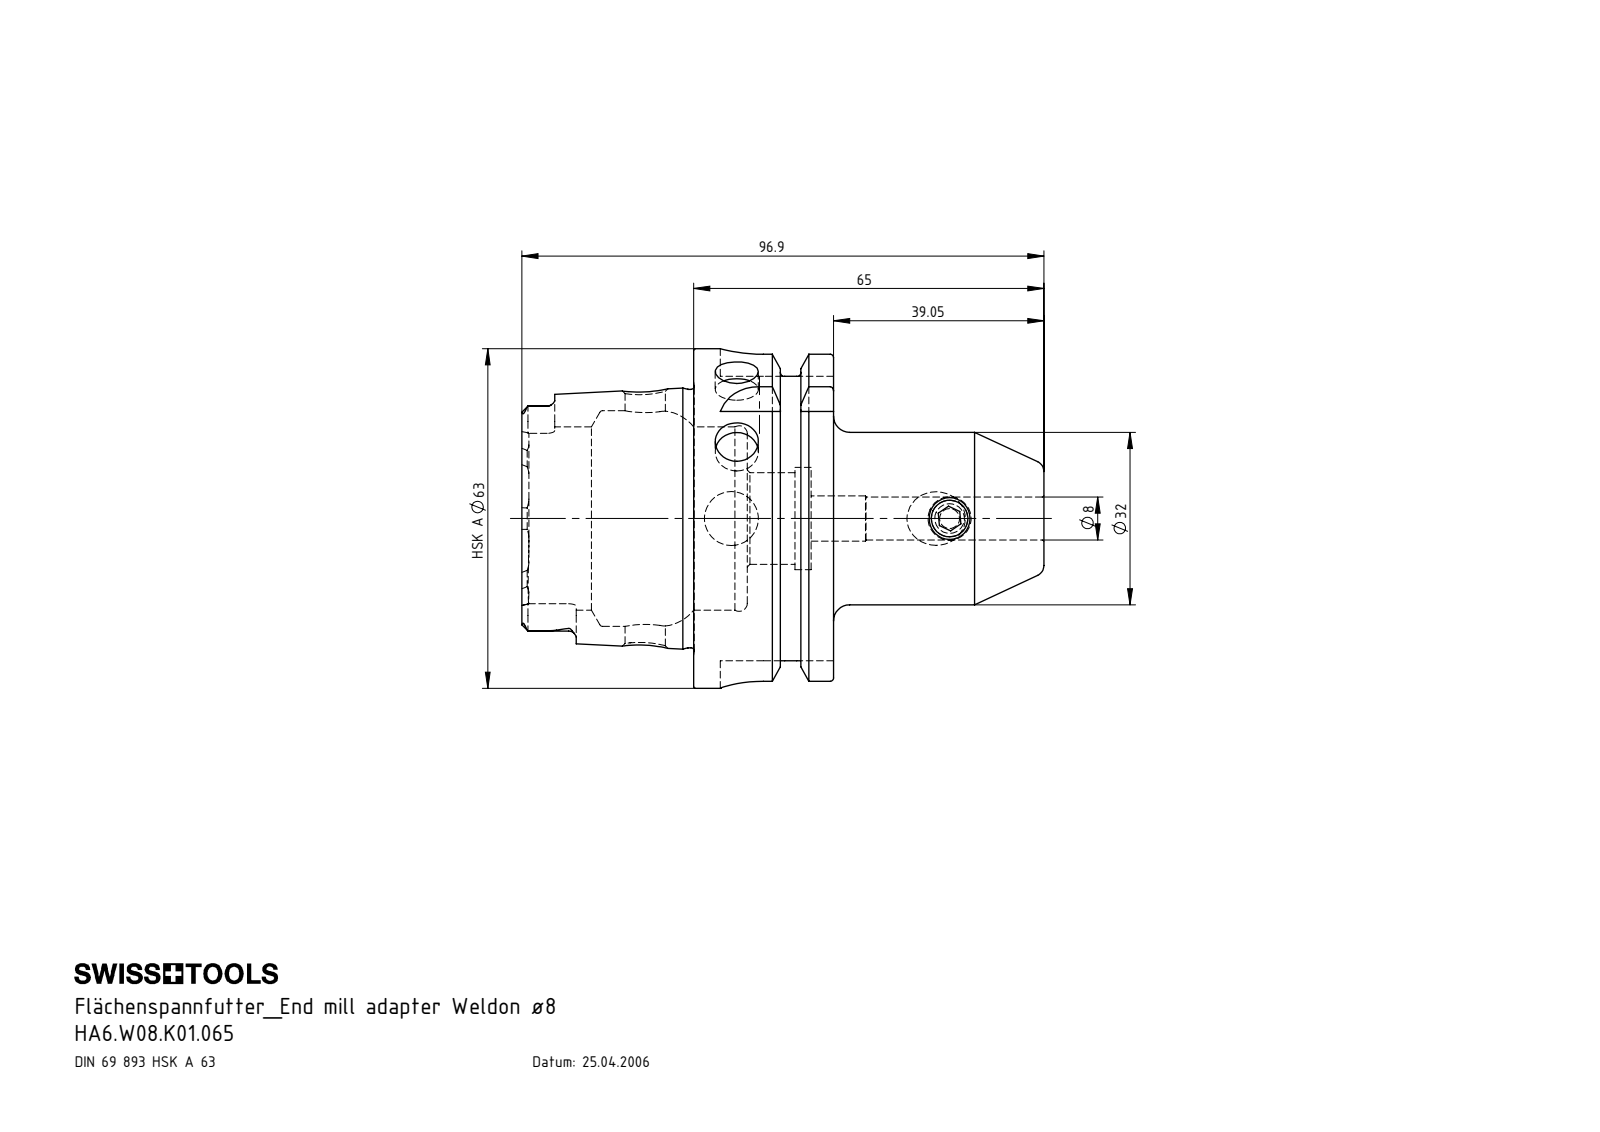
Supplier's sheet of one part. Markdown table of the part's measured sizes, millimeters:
| quantity | value |
| --- | --- |
| part name | HA6-W08.K01.065_B_Fertigbearbeitung; HA6.W08.K01.065; W08-ER1.001.010 |
| STEP written by | SolidWorks 2017 (CONFIG_CONTROL_DESIGN) |
| units | millimeters |
| bodies | 2 solids, 201 faces (57 planar, 55 cylindrical, 89 other) |
| overall size | 96.9 × 63 × 63 |
| volume | 106 859 mm³ |
| surface area | 27 183 mm² |
| round holes (diameter × count) | 8 × 3, 6.8 × 1, 7.5 × 1, 8.4 × 1, 10 × 1, 17 × 1, 19 × 1, 34 × 1, 40 × 1 |
| round bosses / shafts (diameter × count) | 63 × 1, 54.95 × 1, 47.94 × 1, 32 × 1, 8 × 1 |
| partial cylindrical surfaces (radius × count) | 1.4 × 6, 2.88 × 4, 8 × 4 |
| main face-to-face distances | 25.95, 16, 9.95, 31.9, 41.85, 57.85, 52.8, 21.8, 11.85, 53.7 |
| hole center spacings | 40.5 |
